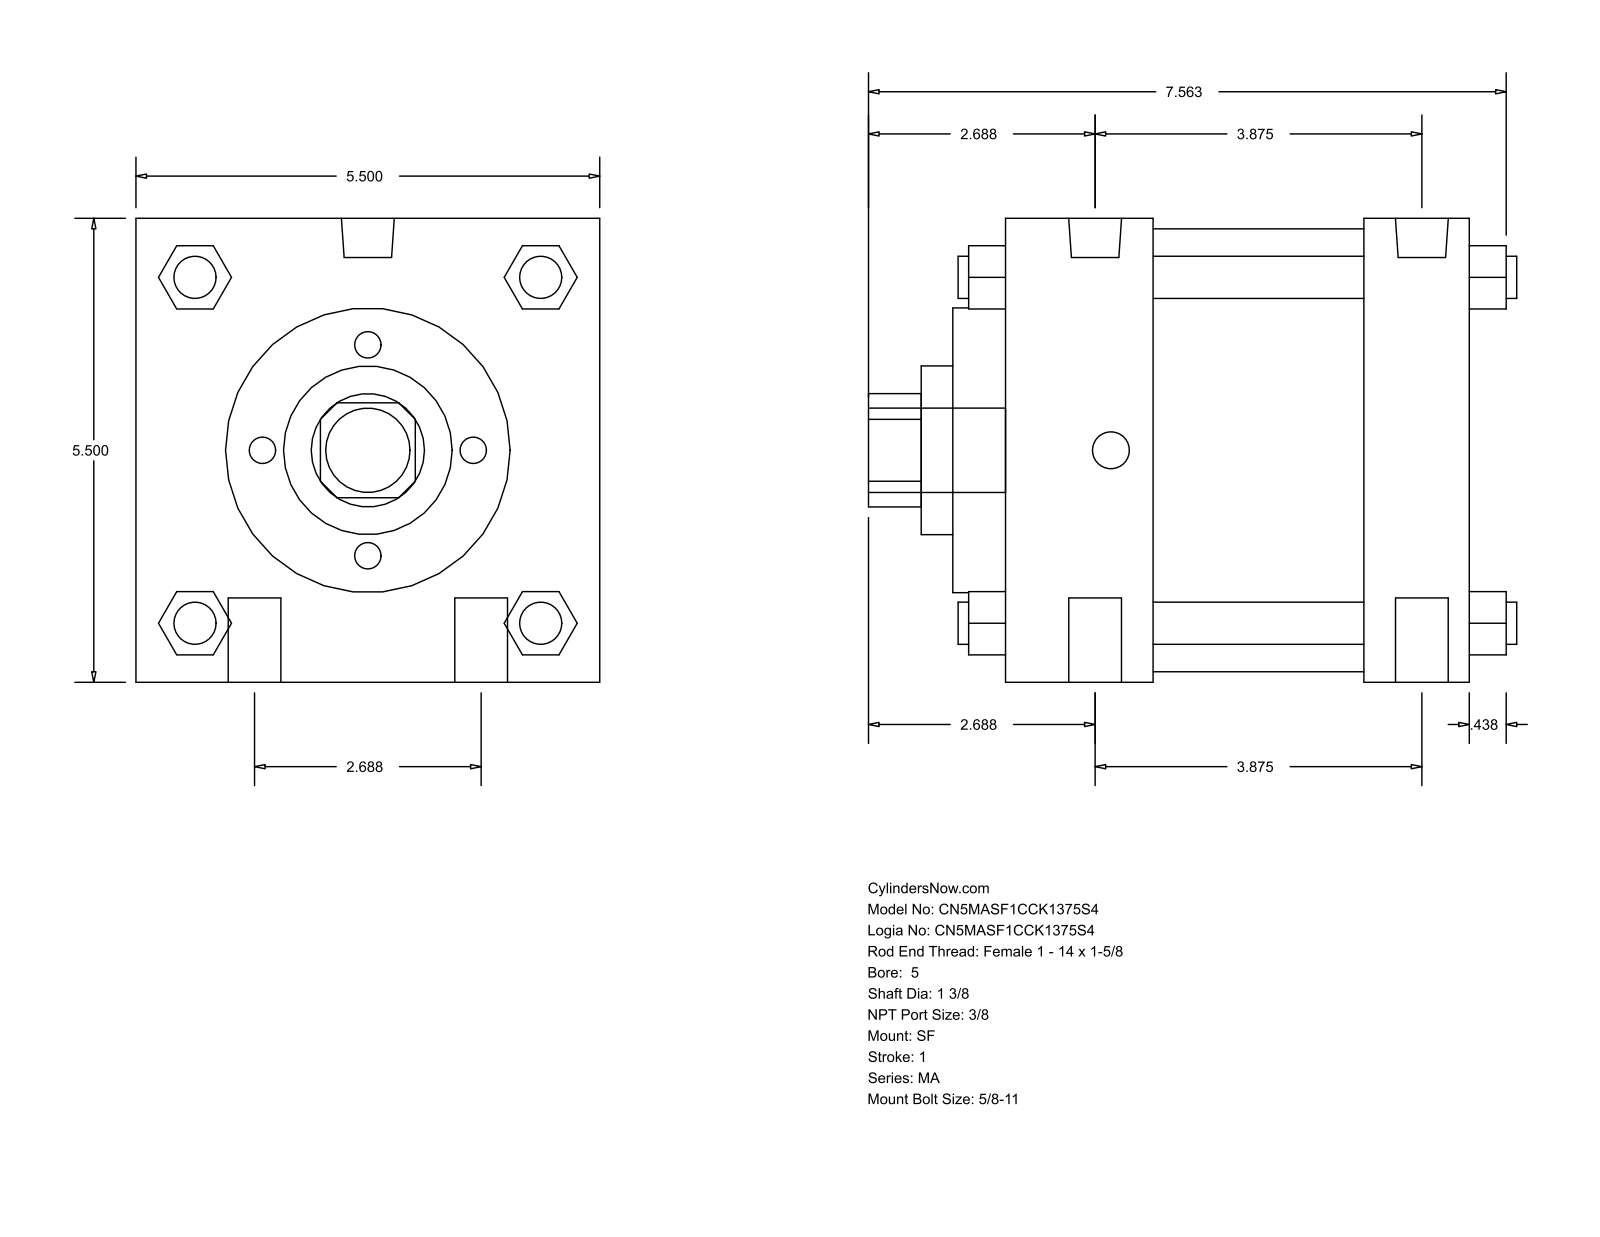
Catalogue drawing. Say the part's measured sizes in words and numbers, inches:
The part is named "MA_SF__0500_1.375". Its 3-D file was written by "GSSL Pune (CONFIG_CONTROL_DESIGN)". It is 0 solids with 126 faces: 95 planar, 31 cylindrical and 0 other. Overall it measures 7.687 by 5.5 by 5.5 inches. Round holes: 1 of diameter 1.375, 1 of diameter 2, 1 of diameter 3.375, 1 of diameter 5.25. Round bosses or shafts: 4 of diameter 0.625, 4 of diameter 0.5, 2 of diameter 0.627, 2 of diameter 0.437, 1 of diameter 1. Partial cylindrical surfaces (rounded edges, fillets, slot ends): 1 of radius 0.672. The main face-to-face distances are 5.5, 1.75, 4.25, 2.5, 3.75, 1.25, 0.625, 2.375, 4.875, 6.125.
